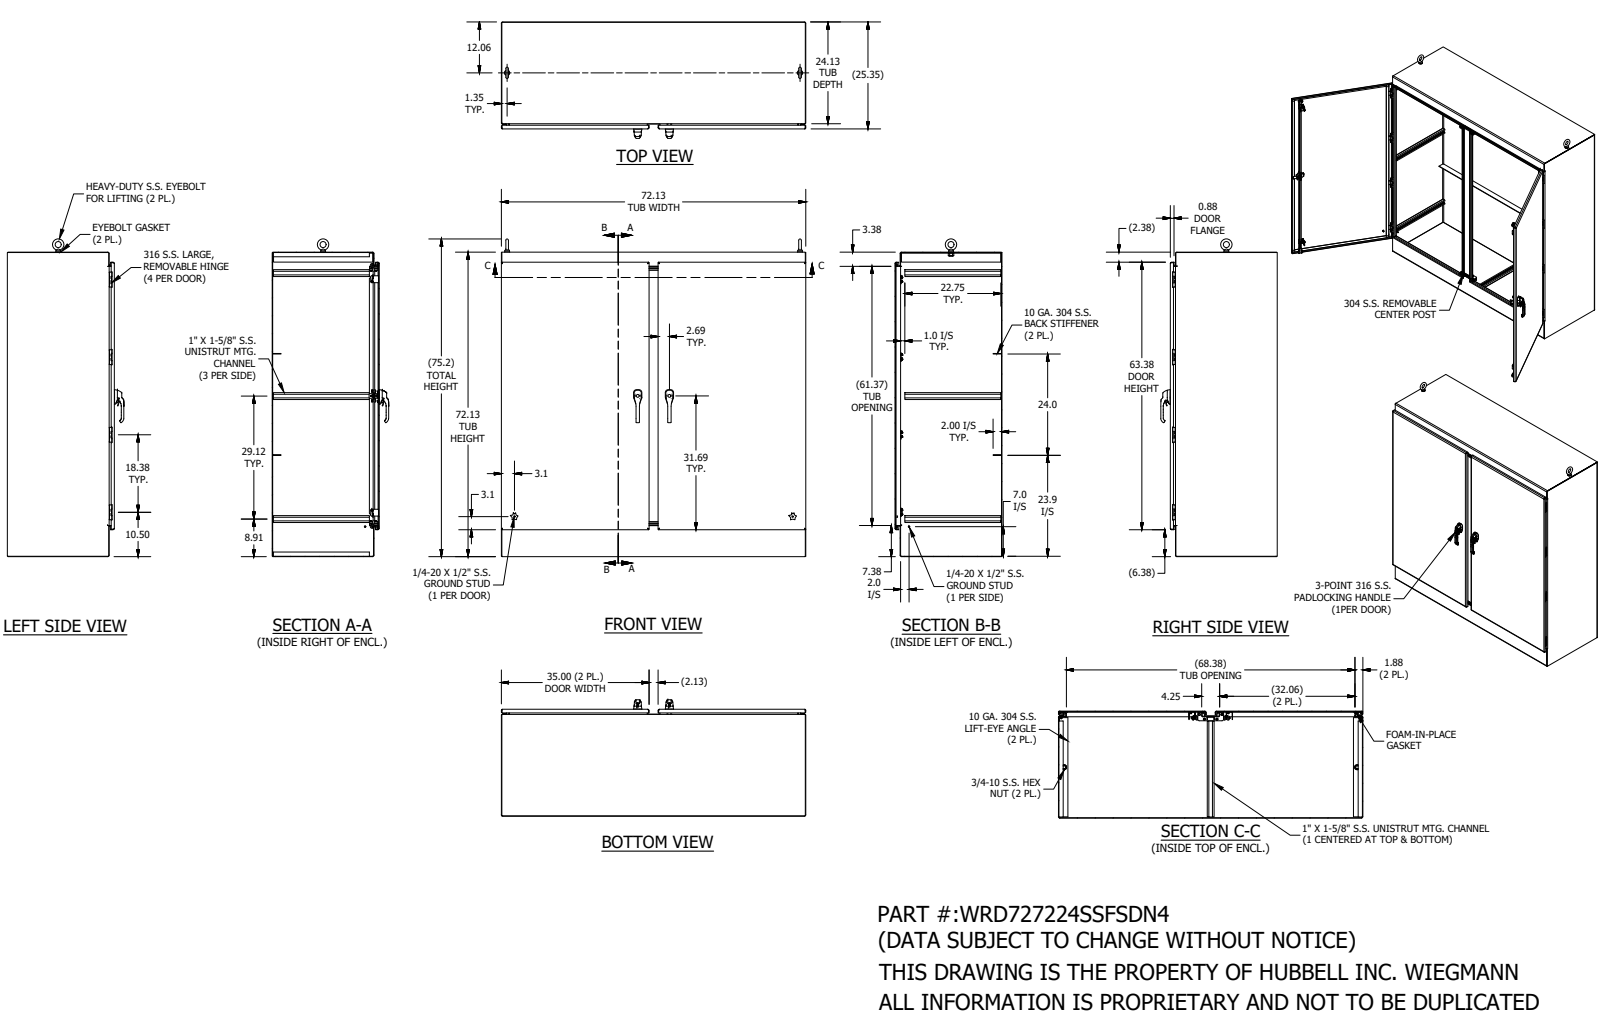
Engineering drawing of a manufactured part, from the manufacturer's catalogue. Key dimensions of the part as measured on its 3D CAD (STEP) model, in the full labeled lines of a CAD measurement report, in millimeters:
Part name (STEP PRODUCT): WRD727224SSFSDN4; WRD727224SSFSDN4BLR; WRD7224SSFSDN4TOP; WRD7224SSFSDN4BTM (+8 more)
STEP written by: Autodesk Inventor 2018 (AUTOMOTIVE_DESIGN)
Units: millimetres
Bodies: 227 solids, 9194 faces (3894 planar, 3238 cylindrical, 2062 other)
Overall size (bounding box): 1911.3 × 1832.2 × 701
Volume: 37 180 000 mm³ · Surface area: 27 150 000 mm²
Round holes (diameter × count): ⌀3.6 ×48, ⌀6.8 ×20, ⌀5 ×16, ⌀7.5 ×16, ⌀16.5 ×16, ⌀3.5 ×8, ⌀4.2 ×8, ⌀4.7 ×8, ⌀5.1 ×8, ⌀6.7 ×8, ⌀5.4 ×6, ⌀7.1 ×6
Round bosses / shafts (diameter × count): ⌀6.4 ×33, ⌀15.9 ×16, ⌀4.6 ×16, ⌀6 ×8, ⌀6 ×6, ⌀25.4 ×4, ⌀14.3 ×4, ⌀13.5 ×4
Partial cylindrical surfaces — rounded edges, fillets, slot ends (radius × count): R0.5 ×344, R0.3 ×229, R1.6 ×64, R3.2 ×58, R0.5 ×42, R2 ×28, R1.3 ×26, R1 ×22
Main face-to-face distances: 2.6, 1829.3, 641.2, 638.6, 2.6, 643.9, 641.2, 1826.7, 1832, 610.1
Hole centre spacings: 224.6, 0.5, 1859.7, 0.6, 0.7, 25.4, 466.7, 933.5
